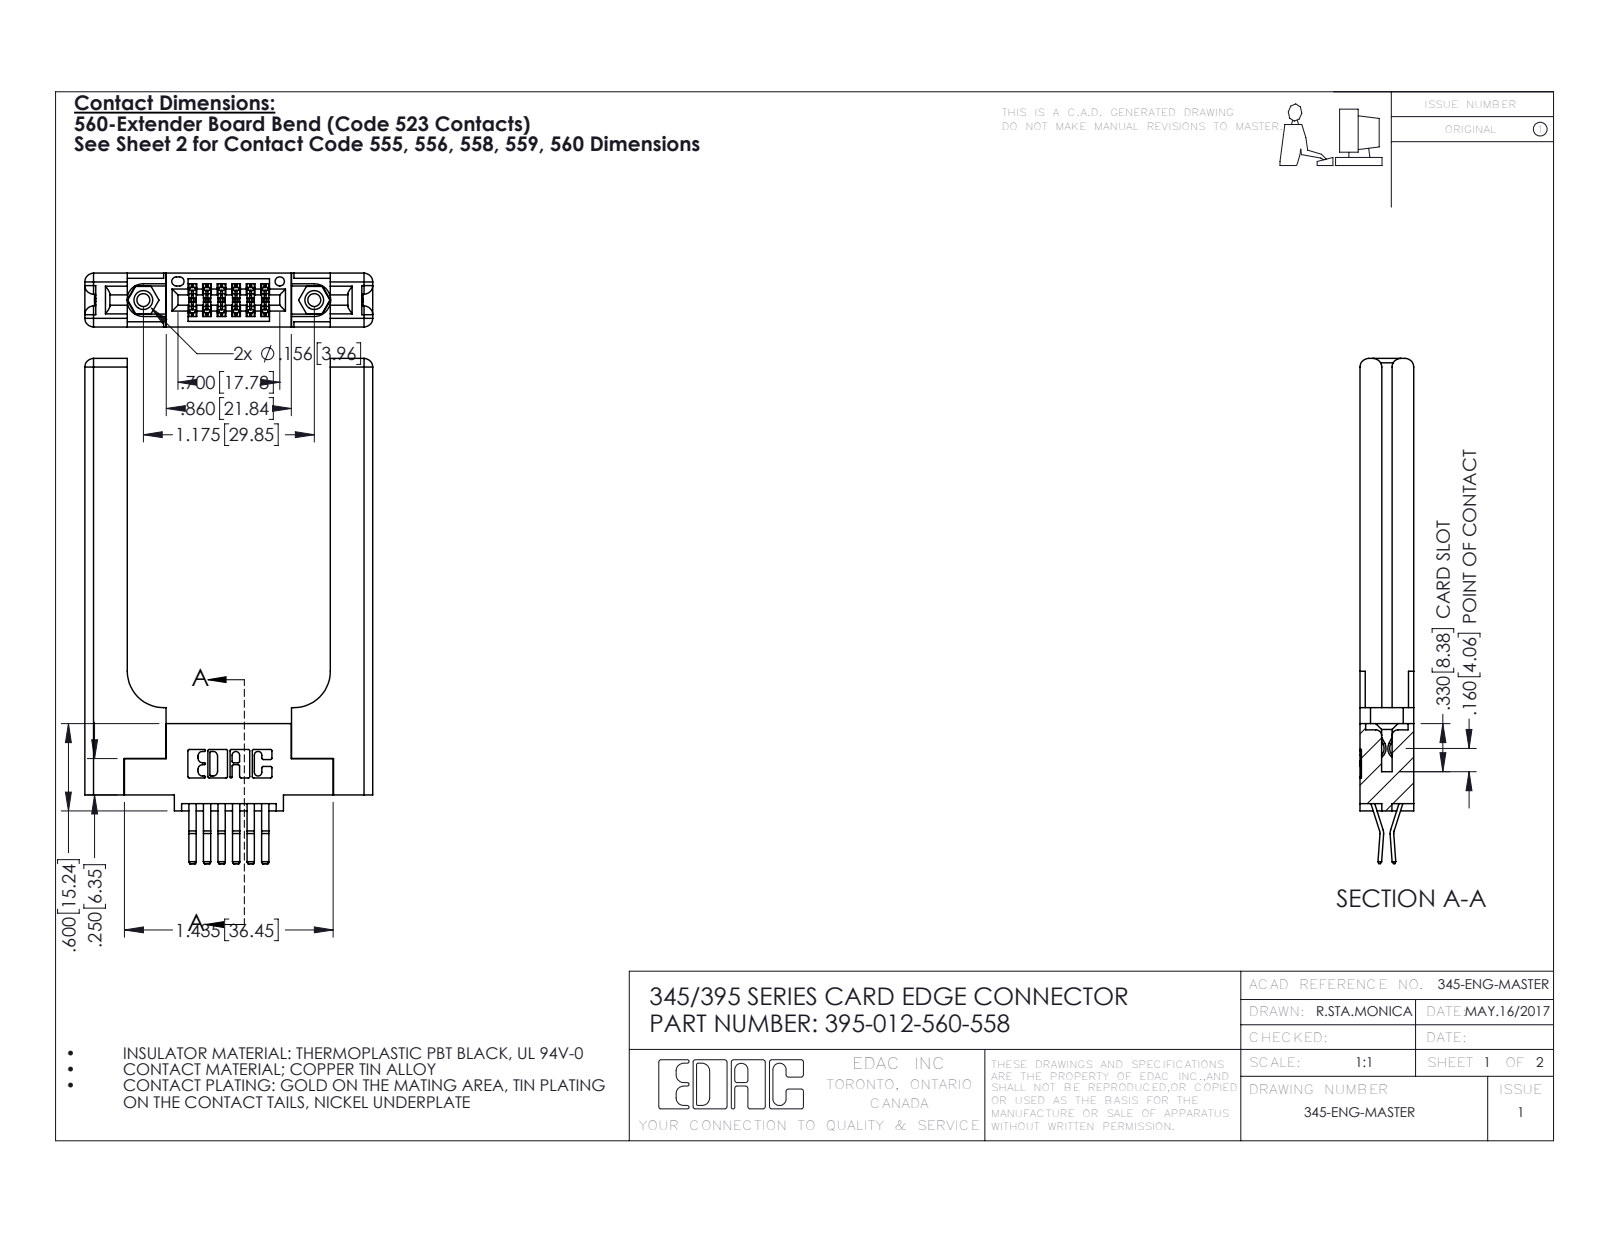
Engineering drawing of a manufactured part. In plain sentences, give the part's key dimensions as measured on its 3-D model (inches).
The part is named "345-250-001_345-250-001-102; 395-012-560-558; 345-220-058_345-220-058; 345-292-001_560 Tail (+1 more)". Its 3-D file was written by "SolidWorks 2016 (CONFIG_CONTROL_DESIGN)". It is 17 solids with 1010 faces: 628 planar, 322 cylindrical and 60 other. Overall it measures 3.472 by 1.979 by 0.37 inches. Its volume is 0.795 cubic inches and its surface area 17.65 square inches. Round holes: 2 of diameter 0.089, 2 of diameter 0.125, 2 of diameter 0.156, 1 of diameter 0.064. Round bosses or shafts: 2 of diameter 0.155. Partial cylindrical surfaces (rounded edges, fillets, slot ends): 22 of radius 0.01, 18 of radius 0.006, 16 of radius 0.06, 6 of radius 0.007, 6 of radius 0.031, 3 of radius 0.026, 2 of radius 0.01, 2 of radius 0.014. The main face-to-face distances are 0.37, 0.15, 0.22, 0.072, 0.148, 0.077, 1.396, 0.298, 0.071, 0.025. The hole center spacings are 0.27, 0.946, 1.175.
